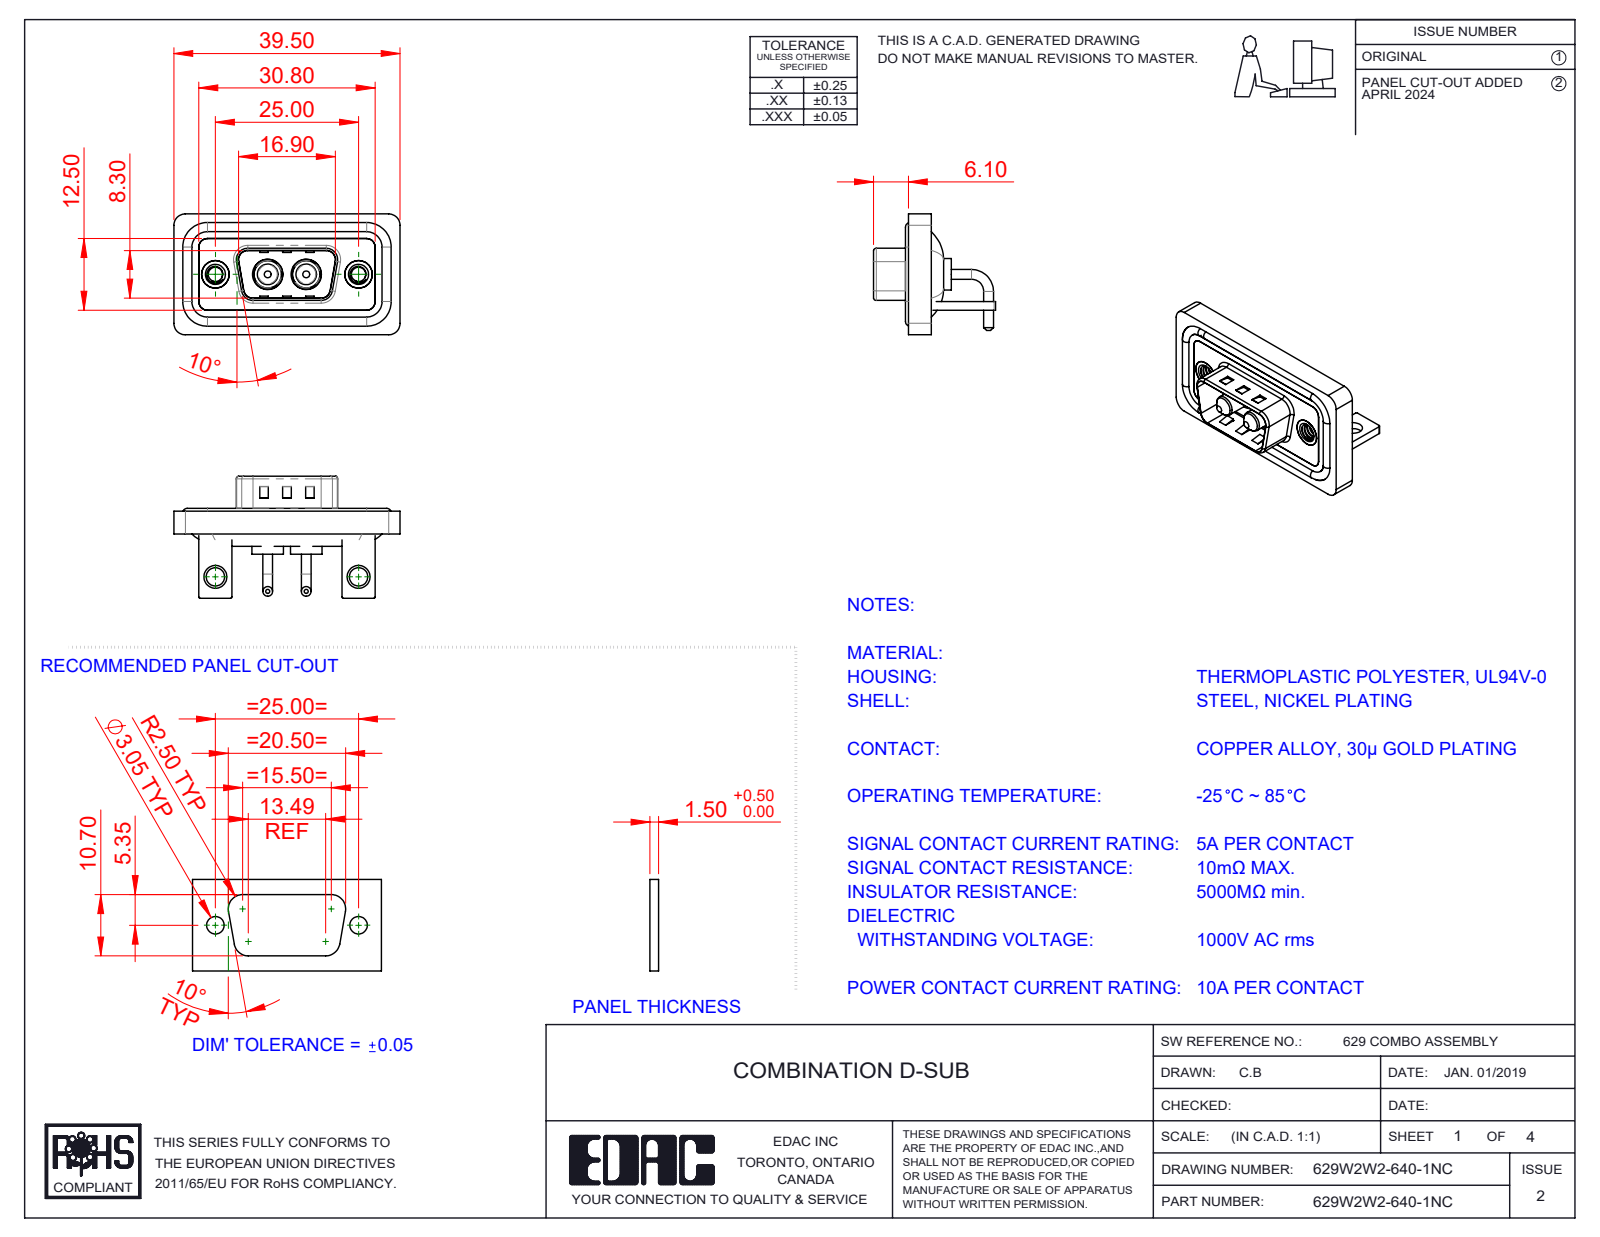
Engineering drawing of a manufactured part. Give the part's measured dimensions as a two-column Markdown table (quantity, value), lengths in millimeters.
| quantity | value |
| --- | --- |
| part name | Power Pin_10A RA; 629Combo Shell Front_09 Contacts; 629Combo Housing_2W2; 629Combo Stabilizer Bracket (+4 more) |
| STEP written by | SolidWorks 2023 (CONFIG_CONTROL_DESIGN) |
| units | millimeters |
| bodies | 13 solids, 535 faces (185 planar, 240 cylindrical, 110 other) |
| overall size | 39.5 × 21.3 × 21.1 |
| volume | 4 740 mm³ |
| surface area | 7 654 mm² |
| round holes (diameter × count) | 2.5 × 2, 3.2 × 2, 4 × 2, 4.8 × 2, 4.85 × 2, 5 × 2, 5.3 × 2 |
| round bosses / shafts (diameter × count) | 1.7 × 4, 1.6 × 4, 5.5 × 2, 5.2 × 2, 4.9 × 2, 4.75 × 2, 3.75 × 2, 3.6 × 2 |
| partial cylindrical surfaces (radius × count) | 2 × 19, 1.5 × 18, 0.25 × 16, 0.5 × 9, 1.6 × 8, 0.6 × 4, 0.65 × 4, 0.9 × 4 |
| main face-to-face distances | 0.4, 1.5, 2.9, 0.8, 1.1, 1.2, 2.1, 1.6, 3.7, 2.5 |
| hole center spacings | 9.14, 15.86, 25, 6.72 |
